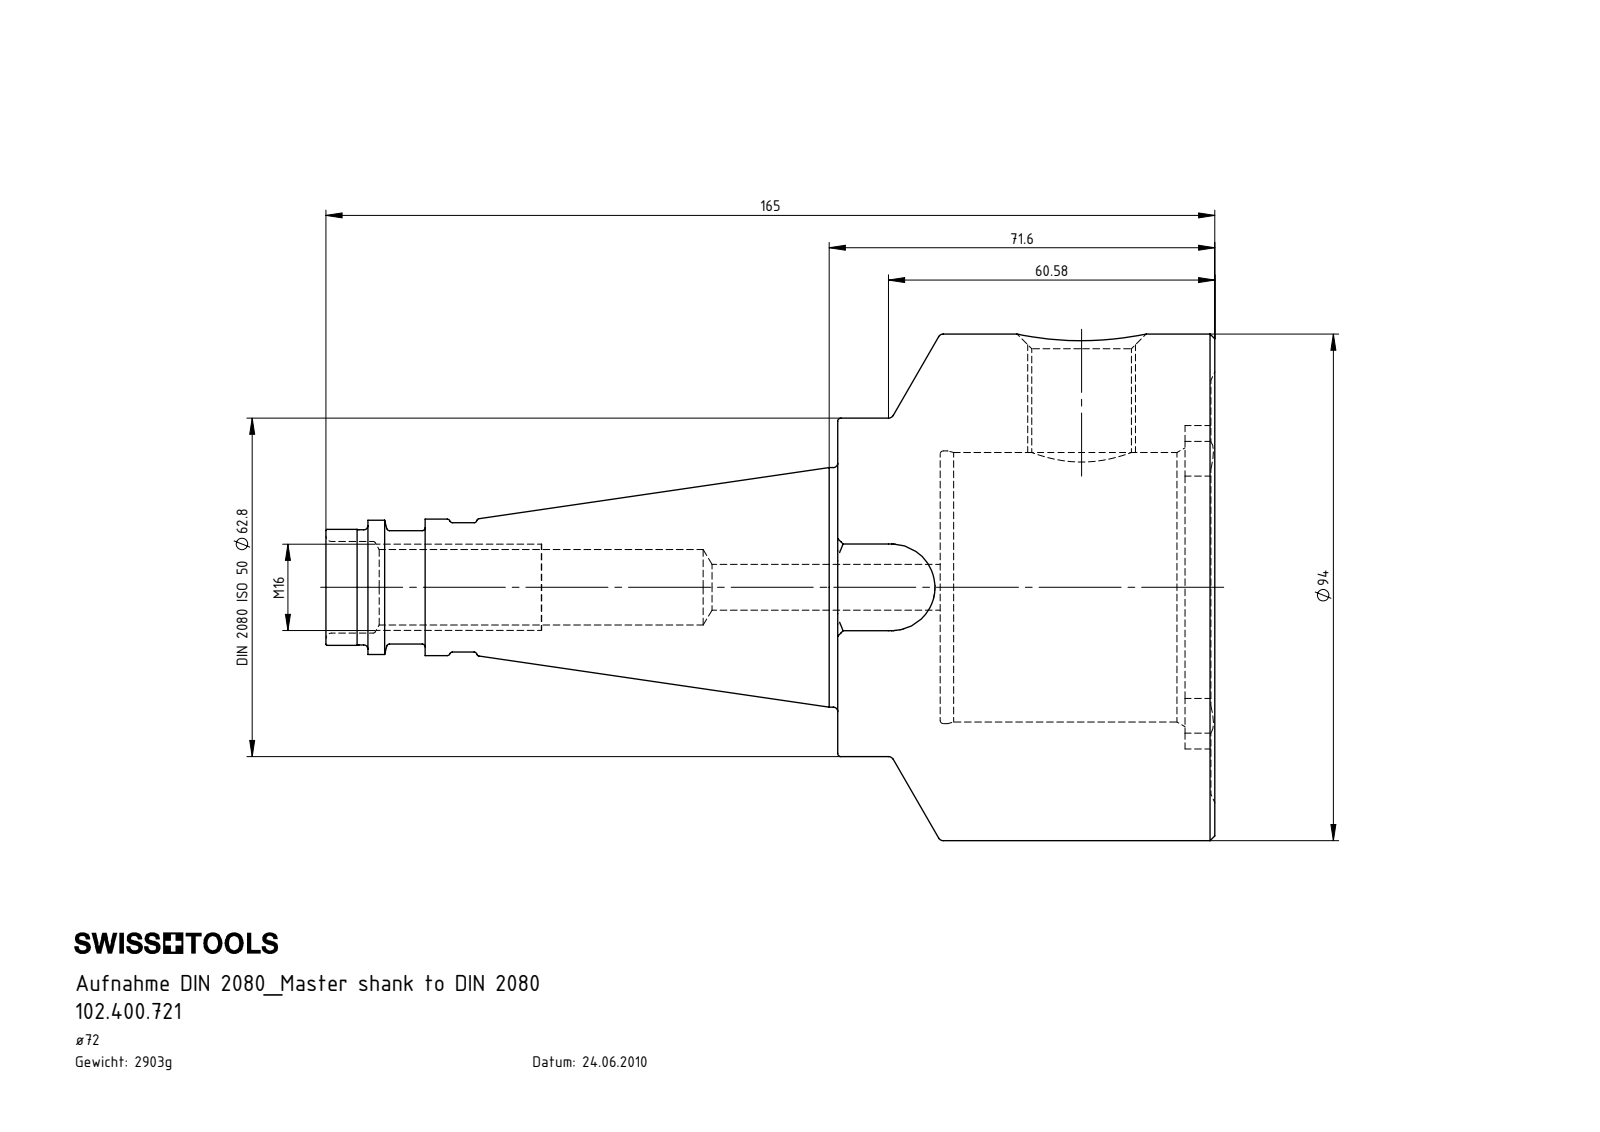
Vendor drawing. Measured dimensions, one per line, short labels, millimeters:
name: 102.400.721
written by: SolidWorks 2017 (CONFIG_CONTROL_DESIGN)
unit: mm
bodies: 1 solid, 137 faces (28 planar, 52 cylindrical, 57 other)
size: 165 × 72 × 72
volume: 272 480 mm³; area: 42 230 mm²
holes: 1× ⌀8.5, 1× ⌀14, 1× ⌀14.5, 1× ⌀17, 1× ⌀40, 1× ⌀40.6
bosses: 1× ⌀72, 1× ⌀62.8, 1× ⌀44.45, 1× ⌀25.3, 1× ⌀24.91, 1× ⌀24, 1× ⌀21.5, 1× ⌀21.35
rounds: 8× R1.6, 4× R5.2, 1× R8.05, 1× R23.75, 1× R28.02
face distances: 29, 70, 41, 64.95, 35.95, 5.05, 69.25, 40.25, 4.3, 0.75
